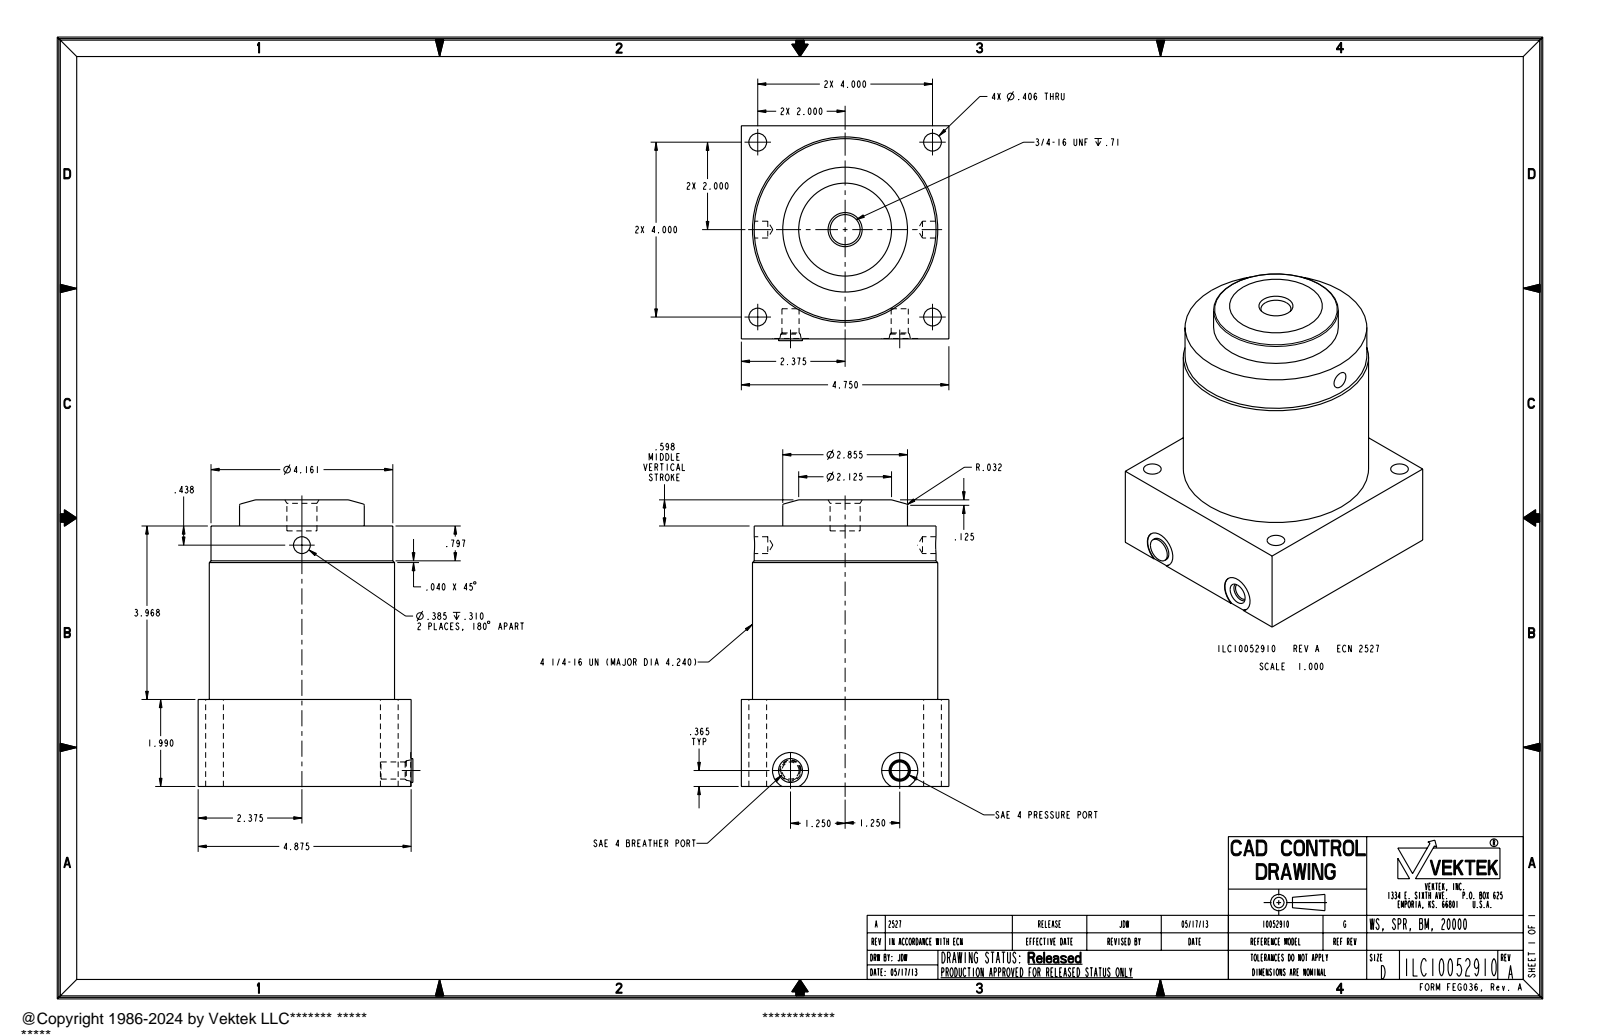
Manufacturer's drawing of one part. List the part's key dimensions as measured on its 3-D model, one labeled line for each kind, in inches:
Part name (STEP PRODUCT): ILC10052910
STEP written by: PRO/ENGINEER BY PARAMETRIC TECHNOLOGY CORPORATION, 2007460 (AUTOMOTIVE_DESIGN_CC2)
Units: inches
Bodies: 1 solid, 63 faces (15 planar, 28 cylindrical, 20 other)
Overall size (bounding box): 6.556 × 4.915 × 4.75
Volume: 103.8 in³ · Surface area: 155 in²
Round holes (diameter × count): ⌀0.406 ×4, ⌀0.392 ×2, ⌀0.825 ×2, ⌀0.385 ×1, ⌀0.688 ×1
Round bosses / shafts (diameter × count): ⌀4.24 ×1, ⌀4.161 ×1, ⌀2.855 ×1, ⌀0.547 ×1
Main face-to-face distances: 4.75, 1.99, 4.875, 5.958, 3.968, 6.556, 4.566, 0.598, 4.865, 5.846
Hole centre spacings: 2.828, 4, 5.657, 2.5
